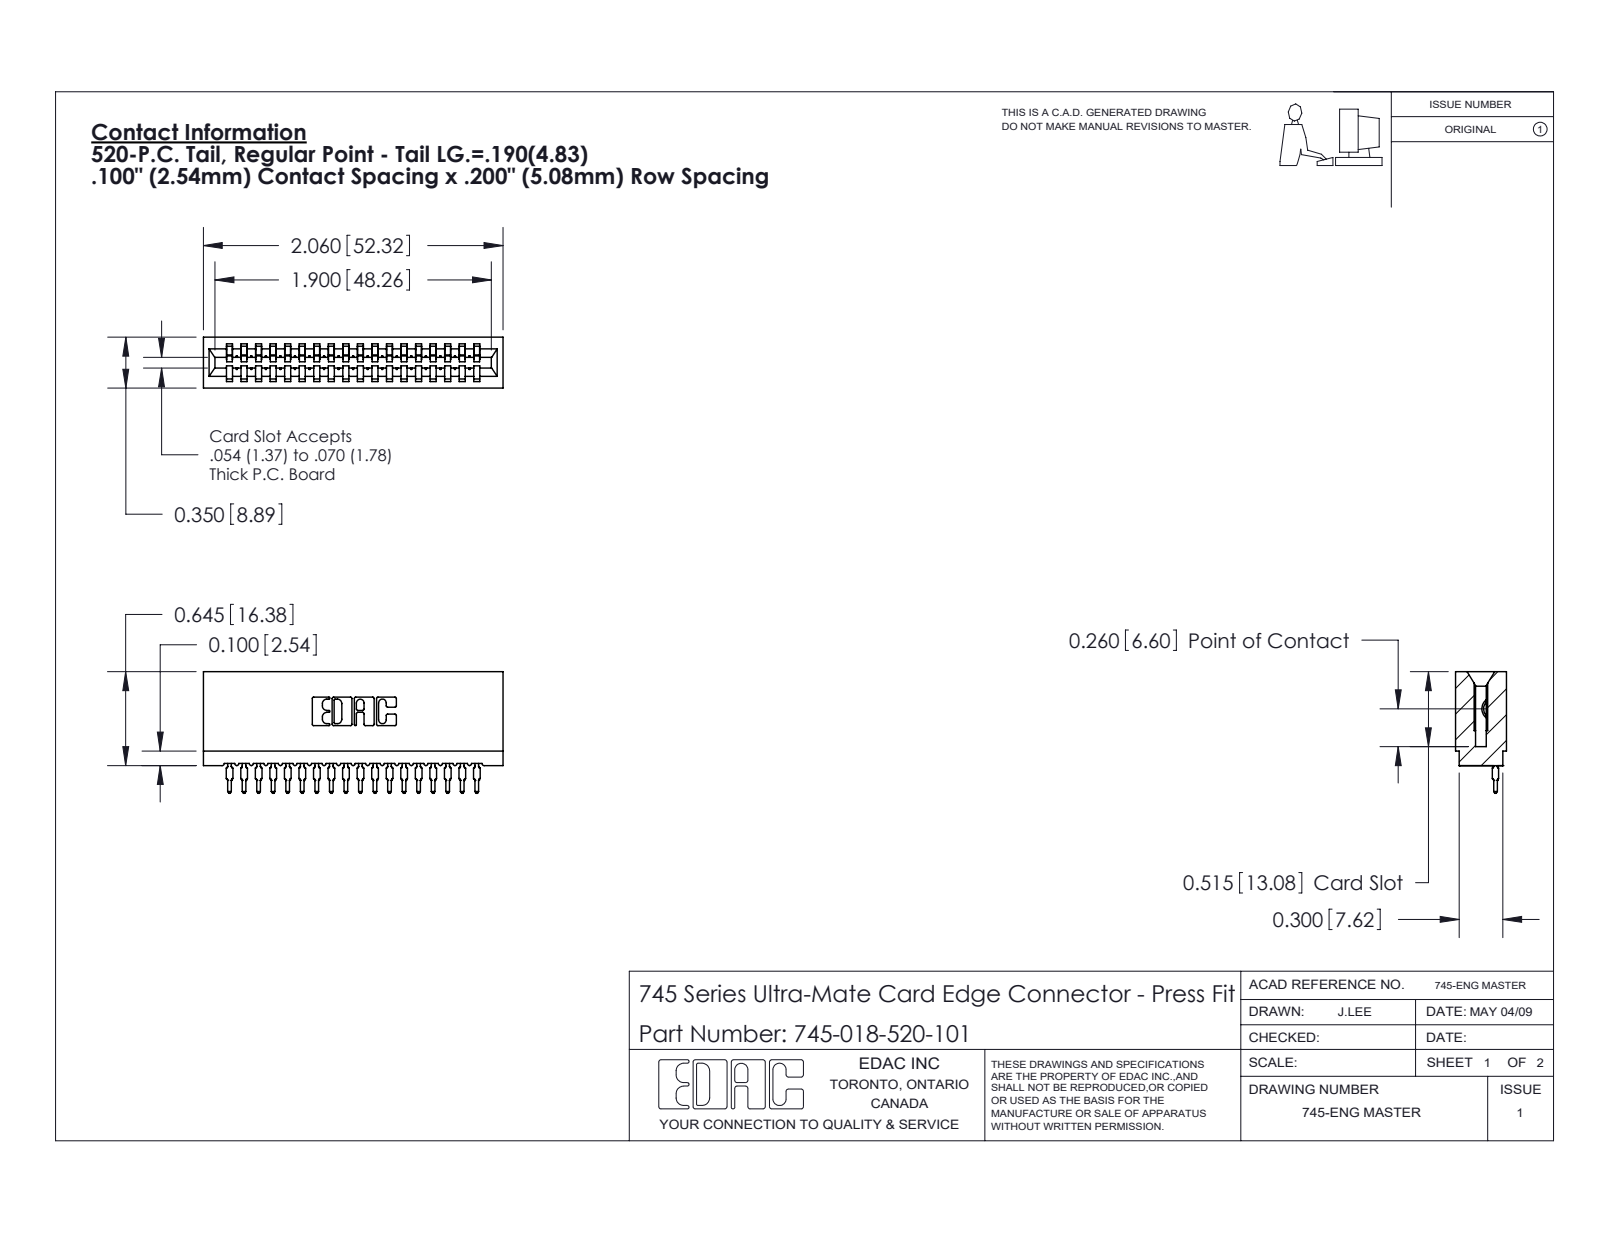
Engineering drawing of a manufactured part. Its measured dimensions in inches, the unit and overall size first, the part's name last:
Units: inches
Overall size (bounding box): 2.06 × 0.836 × 0.35
Partial cylindrical surfaces — rounded edges, fillets, slot ends (radius × count): R0.015 ×36, R0.021 ×36, R0.01 ×22, R0.007 ×6, R0.031 ×6, R0.005 ×4, R0.011 ×4, R0.026 ×3
Main face-to-face distances: 0.1, 0.2, 0.3, 0.4, 0.5, 0.35, 0.6, 0.138, 0.212, 0.045
Volume: 0.285 in³ · Surface area: 12.58 in²
Bodies: 19 solids, 2111 faces (1261 planar, 382 cylindrical, 468 other)
Part name (STEP PRODUCT): 745-292-001_520; 745 Part_Insulator Option - 01; 745-018-520-101
STEP written by: SolidWorks 2020 (CONFIG_CONTROL_DESIGN)
